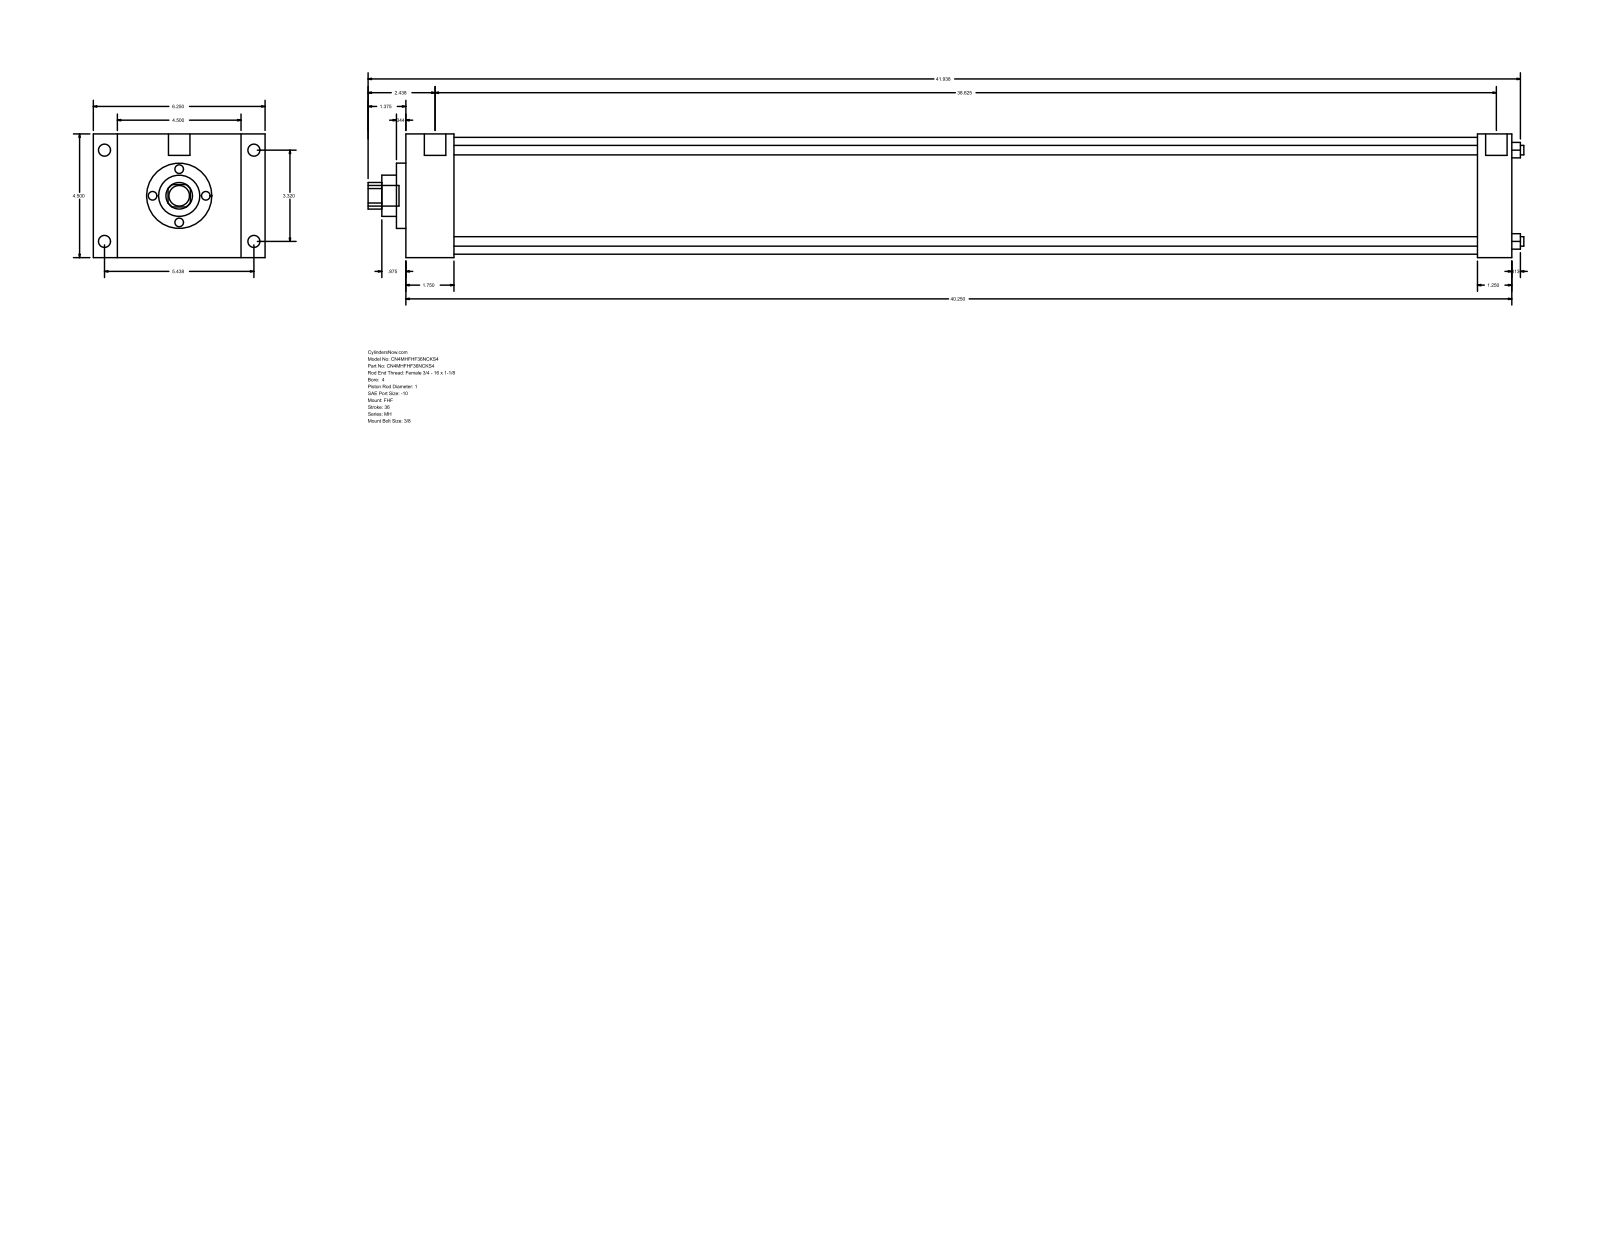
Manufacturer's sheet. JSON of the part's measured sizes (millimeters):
{"part_name": "MH_FHF__0400_1", "step_written_by": "GSSL Pune (CONFIG_CONTROL_DESIGN)", "units": "millimeters", "bodies": {"solids": 0, "faces": 90, "planar": 61, "cylindrical": 29, "other": 0}, "overall_size": [1068.39, 158.75, 114.3], "round_holes": [[8.76, 4], [25.4, 1], [38.1, 1], [60.33, 1], [107.95, 1]], "round_bosses_or_shafts": [[11.13, 4], [8.73, 4], [19.84, 2], [19.05, 1]], "partial_cylinders_radius": [[12.29, 1]], "face_to_face_distances": [114.3, 1022.36, 44.46, 977.9, 22.23, 136.53, 158.76, 990.61, 946.15, 31.75], "hole_center_spacings": [59.62, 84.32, 119.25]}
